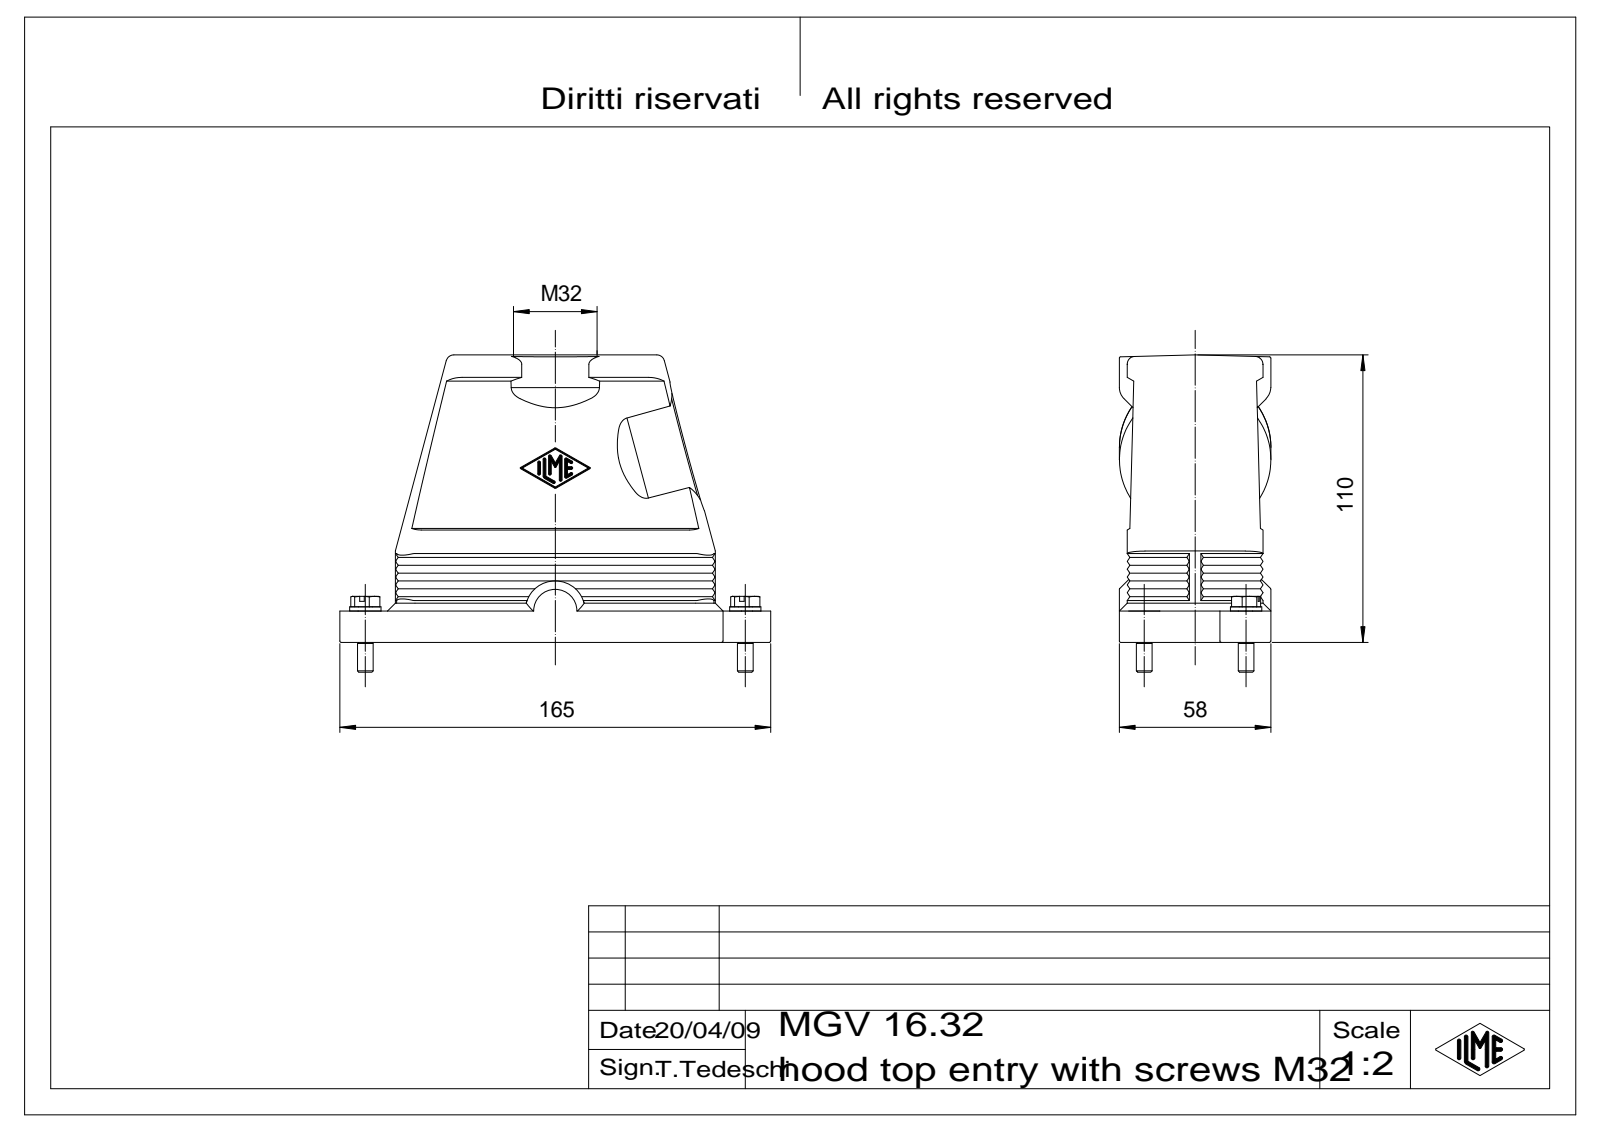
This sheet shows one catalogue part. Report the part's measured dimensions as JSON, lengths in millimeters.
{"part_name": "MGV 16.32", "step_written_by": "Autodesk Inventor 7 (AUTOMOTIVE_DESIGN)", "units": "millimeters", "bodies": {"solids": 3, "faces": 767, "planar": 189, "cylindrical": 195, "other": 383}, "overall_size": [165, 122.2, 58], "volume_mm3": 232504, "surface_area_mm2": 91473, "round_holes": [[2.46, 2], [3.2, 2], [6.6, 2], [15, 2], [32, 1]], "round_bosses_or_shafts": [[58, 2], [56, 2], [12.5, 2], [6, 2]], "partial_cylinders_radius": [[0.5, 39], [0.75, 14], [7.5, 8], [6, 6], [1.5, 4], [3, 4], [5.75, 2], [10.5, 2]], "face_to_face_distances": [3, 52, 49, 6, 46, 55, 2.5, 0.5, 58, 3.5], "hole_center_spacings": [34.69, 116.38, 82.07, 150.86]}
